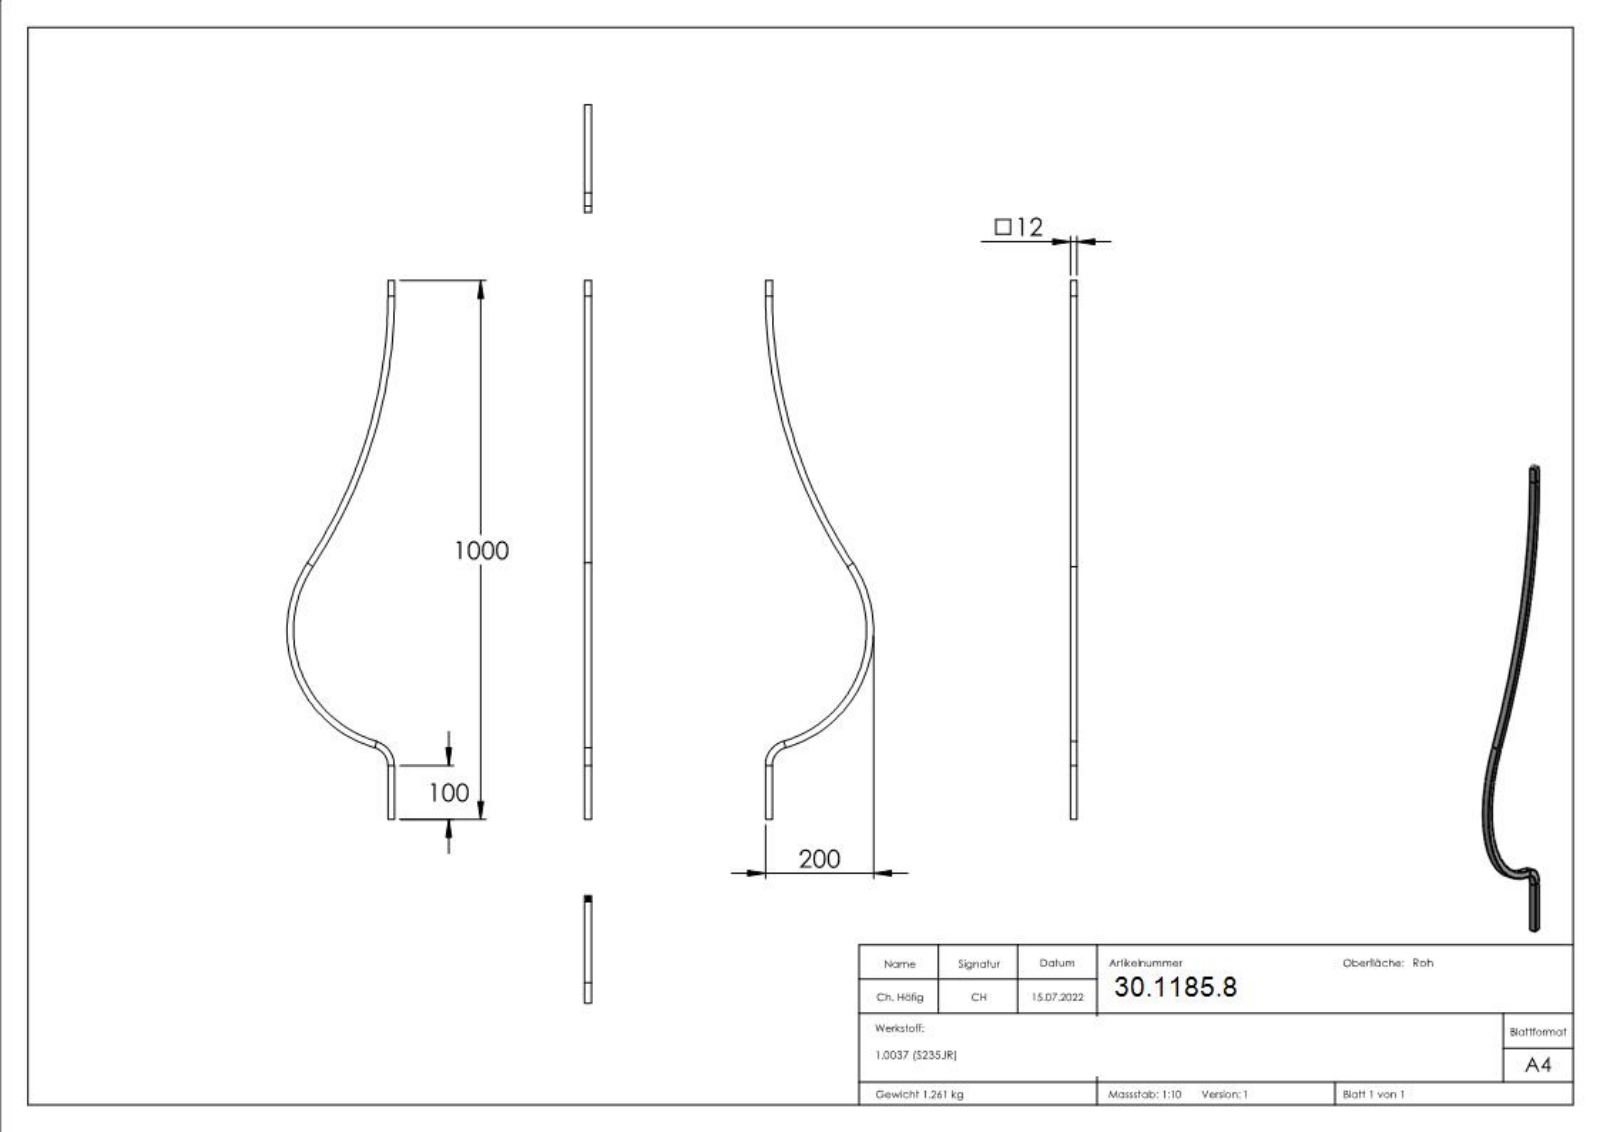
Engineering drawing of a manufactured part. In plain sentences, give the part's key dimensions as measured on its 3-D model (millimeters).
The part is named "1713-G". Its 3-D file was written by "SolidWorks 2018 (CONFIG_CONTROL_DESIGN)". It is 1 solid with 236 faces: 139 planar, 6 cylindrical and 91 other. Overall it measures 1000 by 200 by 12 millimeters. Its volume is 161 695 cubic millimeters and its surface area 54 197 square millimeters. Partial cylindrical surfaces (rounded edges, fillets, slot ends): 1 of radius 34, 1 of radius 46, 1 of radius 214, 1 of radius 226, 1 of radius 894, 1 of radius 906. The main face-to-face distances are 12, 1000, 999.9, 1.84, 1.62, 1.48, 2.01, 3.27, 5.36, 0.36.
